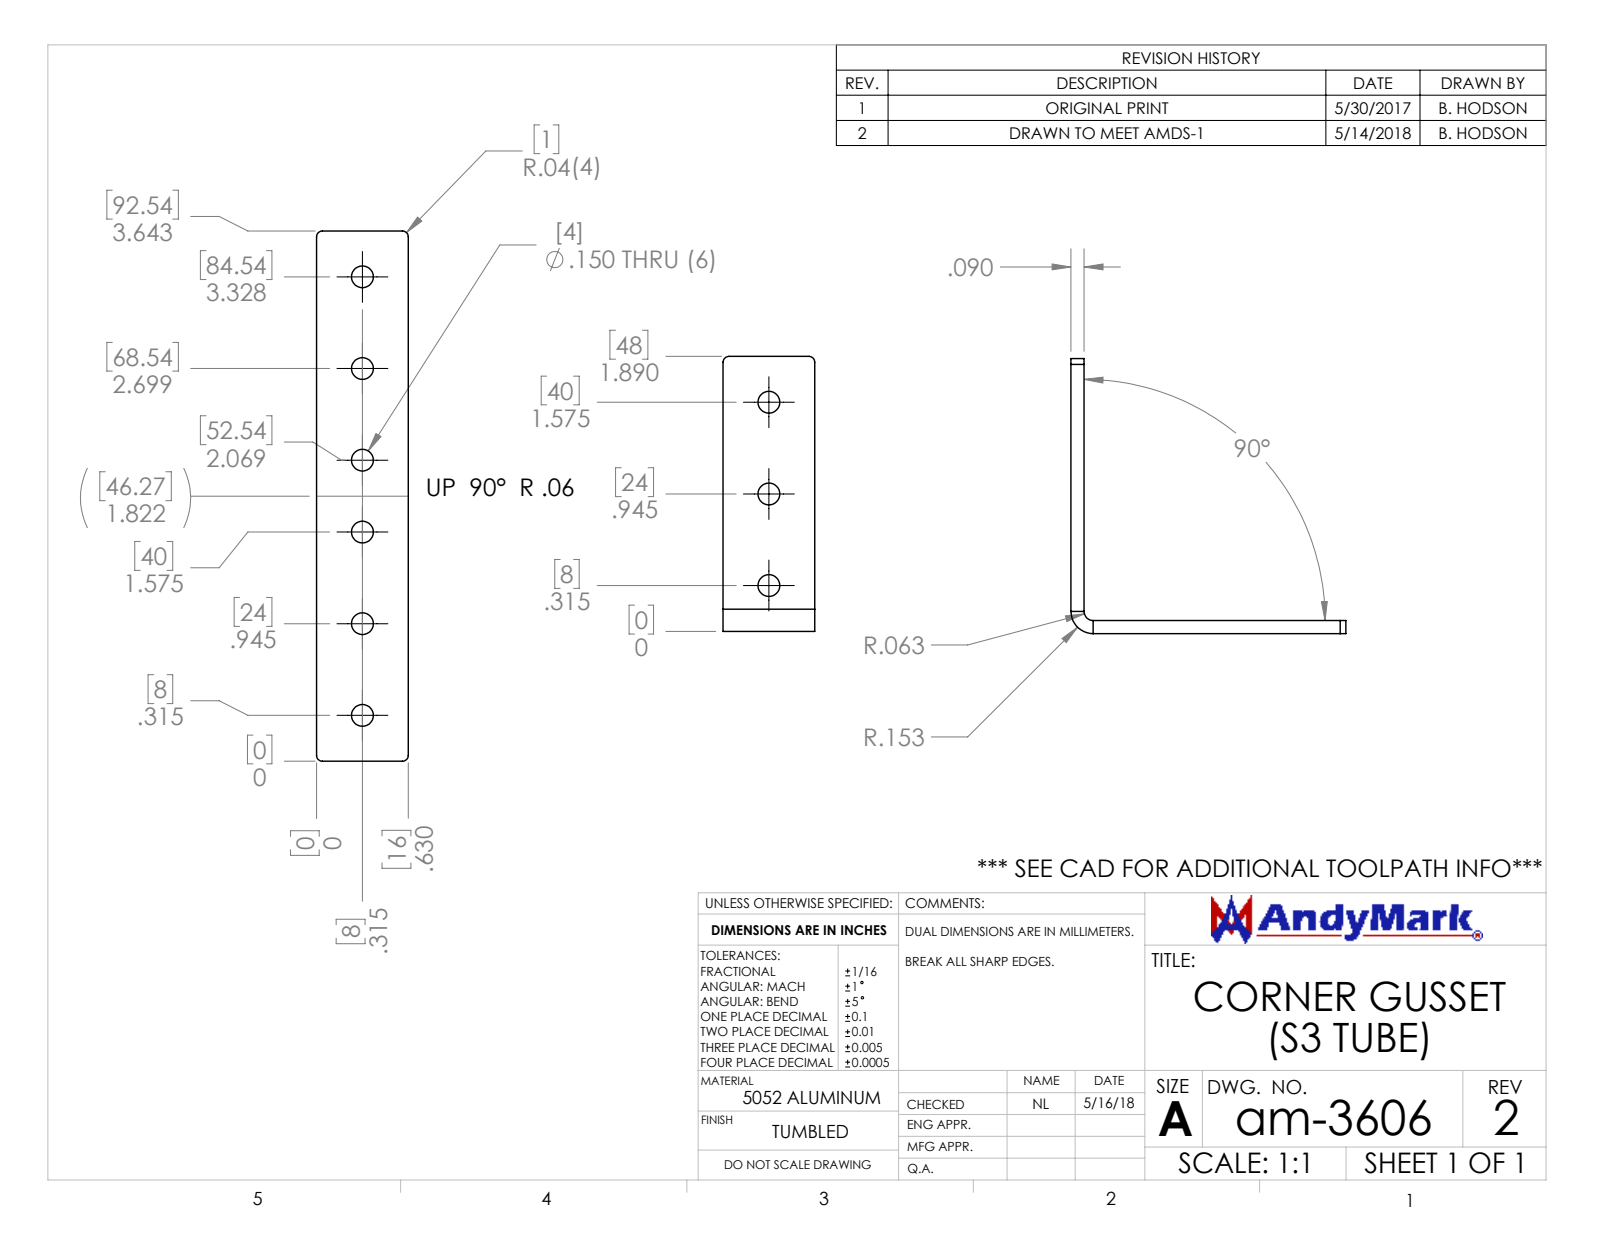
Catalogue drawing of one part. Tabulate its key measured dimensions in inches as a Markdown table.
| quantity | value |
| --- | --- |
| part name | am-3606 Corner Gusset (S3 Tube) REV2 |
| STEP written by | SolidWorks 2017 (AUTOMOTIVE_DESIGN) |
| units | inches |
| bodies | 1 solid, 30 faces (12 planar, 18 cylindrical, 0 other) |
| overall size | 1.89 × 1.89 × 0.63 |
| volume | 0.197 in³ |
| surface area | 5.392 in² |
| round holes (diameter × count) | 0.15 × 6 |
| partial cylindrical surfaces (radius × count) | 0.039 × 4, 0.063 × 1, 0.152 × 1 |
| main face-to-face distances | 0.09, 0.63, 1.89, 1.8 |
| hole center spacings | 0.63, 1.26 |
